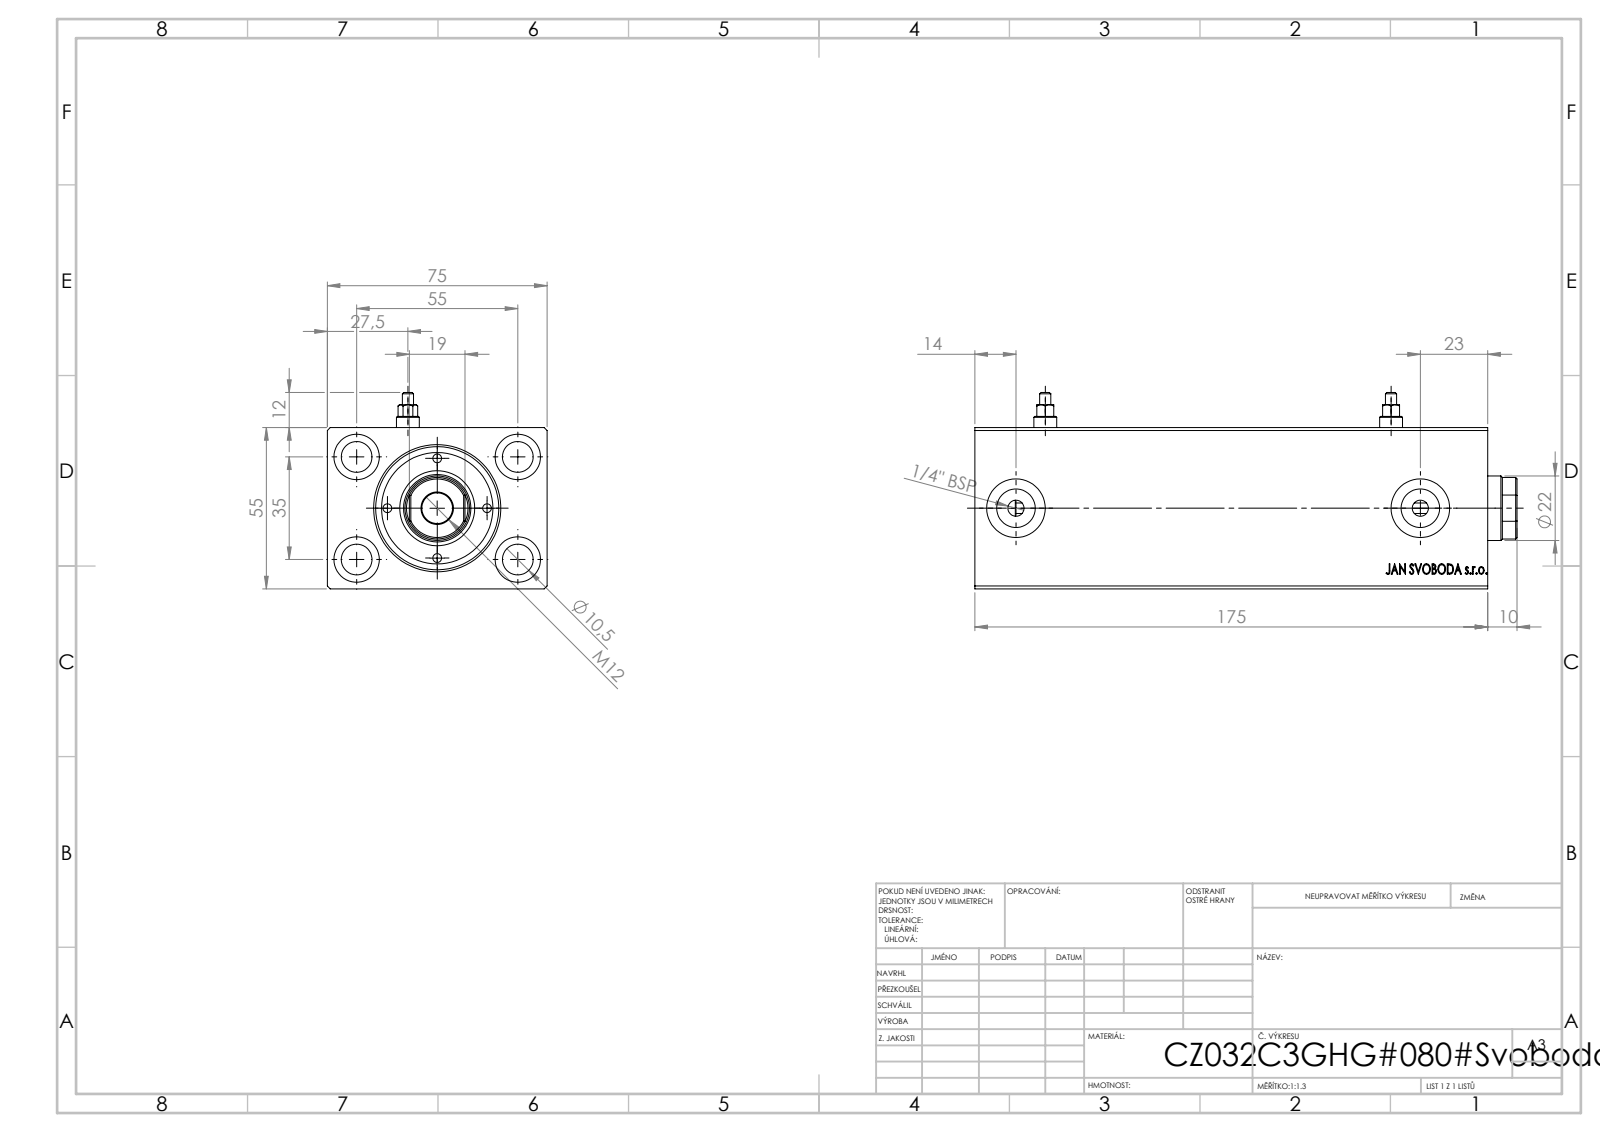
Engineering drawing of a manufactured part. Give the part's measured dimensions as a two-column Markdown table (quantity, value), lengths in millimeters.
| quantity | value |
| --- | --- |
| STEP written by | SolidWorks 2019 (CONFIG_CONTROL_DESIGN) |
| units | millimeters |
| bodies | 1 solid, 826 faces (398 planar, 46 cylindrical, 382 other) |
| overall size | 175 × 75 × 55 |
| volume | 512 603 mm³ |
| surface area | 95 035 mm² |
| round holes (diameter × count) | 10.5 × 4, 15.5 × 4, 5.5 × 2, 8 × 2, 13.16 × 2, 20 × 2, 32 × 1, 36 × 1, 42 × 1 |
| main face-to-face distances | 55, 75, 175, 13.6, 174.8, 10.33, 164.67, 161.2, 13.8, 10 |
| hole center spacings | 32.6, 35, 55, 65.19, 118, 138 |
